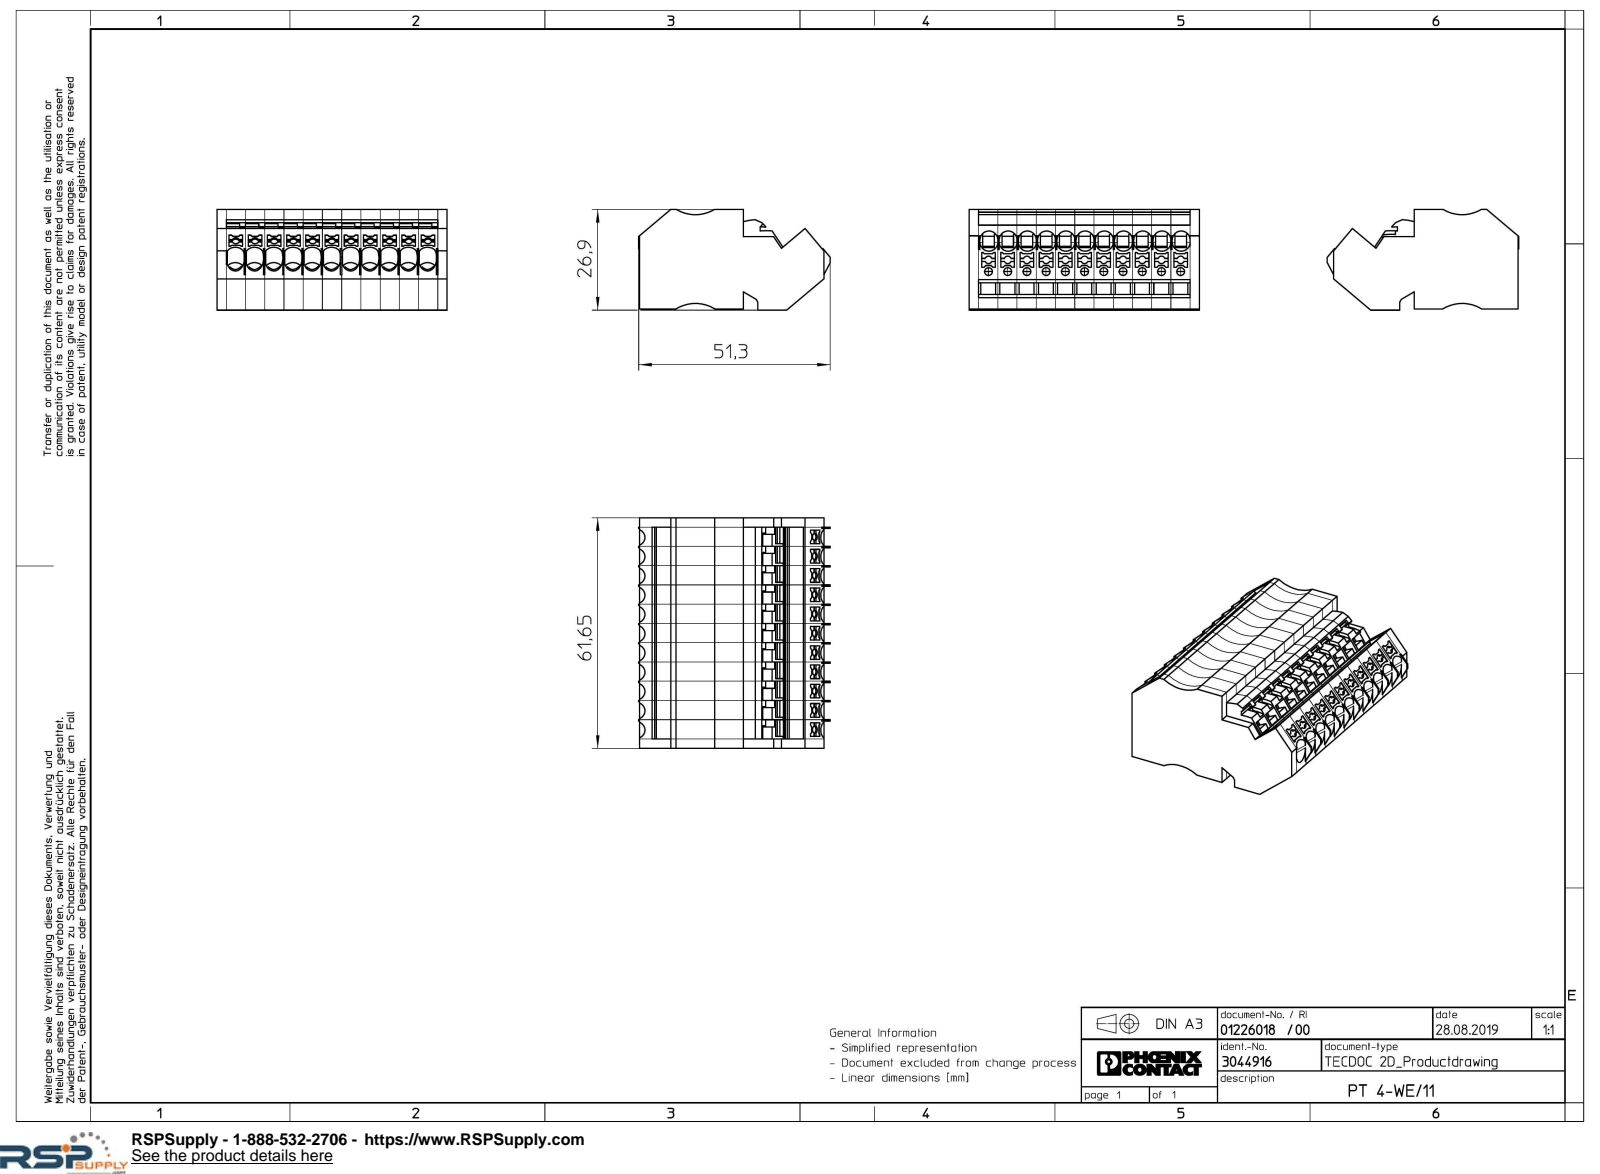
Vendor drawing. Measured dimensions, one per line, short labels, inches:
name: PT_4_WE_11-select
written by: Creo Elements/Direct Modeling 20.1A 29-Sep-2018 (C) Parametric Technology GmbH (AUTOMOTIVE_DESIGN)
unit: in
bodies: 1 solid, 1855 faces (1609 planar, 224 cylindrical, 22 other)
size: 2.427 × 2.02 × 1.059
volume: 3.4 in³; area: 33.75 in²
holes: 11× ⌀0.083
rounds: 44× R0.094, 22× R0.039, 3× R0.041, 2× R0.394, 1× R0.041, 1× R0.07, 1× R0.488, 1× R0.527
face distances: 2.427, 0.203, 0.124, 0.152, 0.276, 0.406, 1.094, 0.608, 0.283, 0.772
hole spacings: 0.203, 0.406, 0.608, 0.811, 1.014, 1.217, 1.419, 1.622
